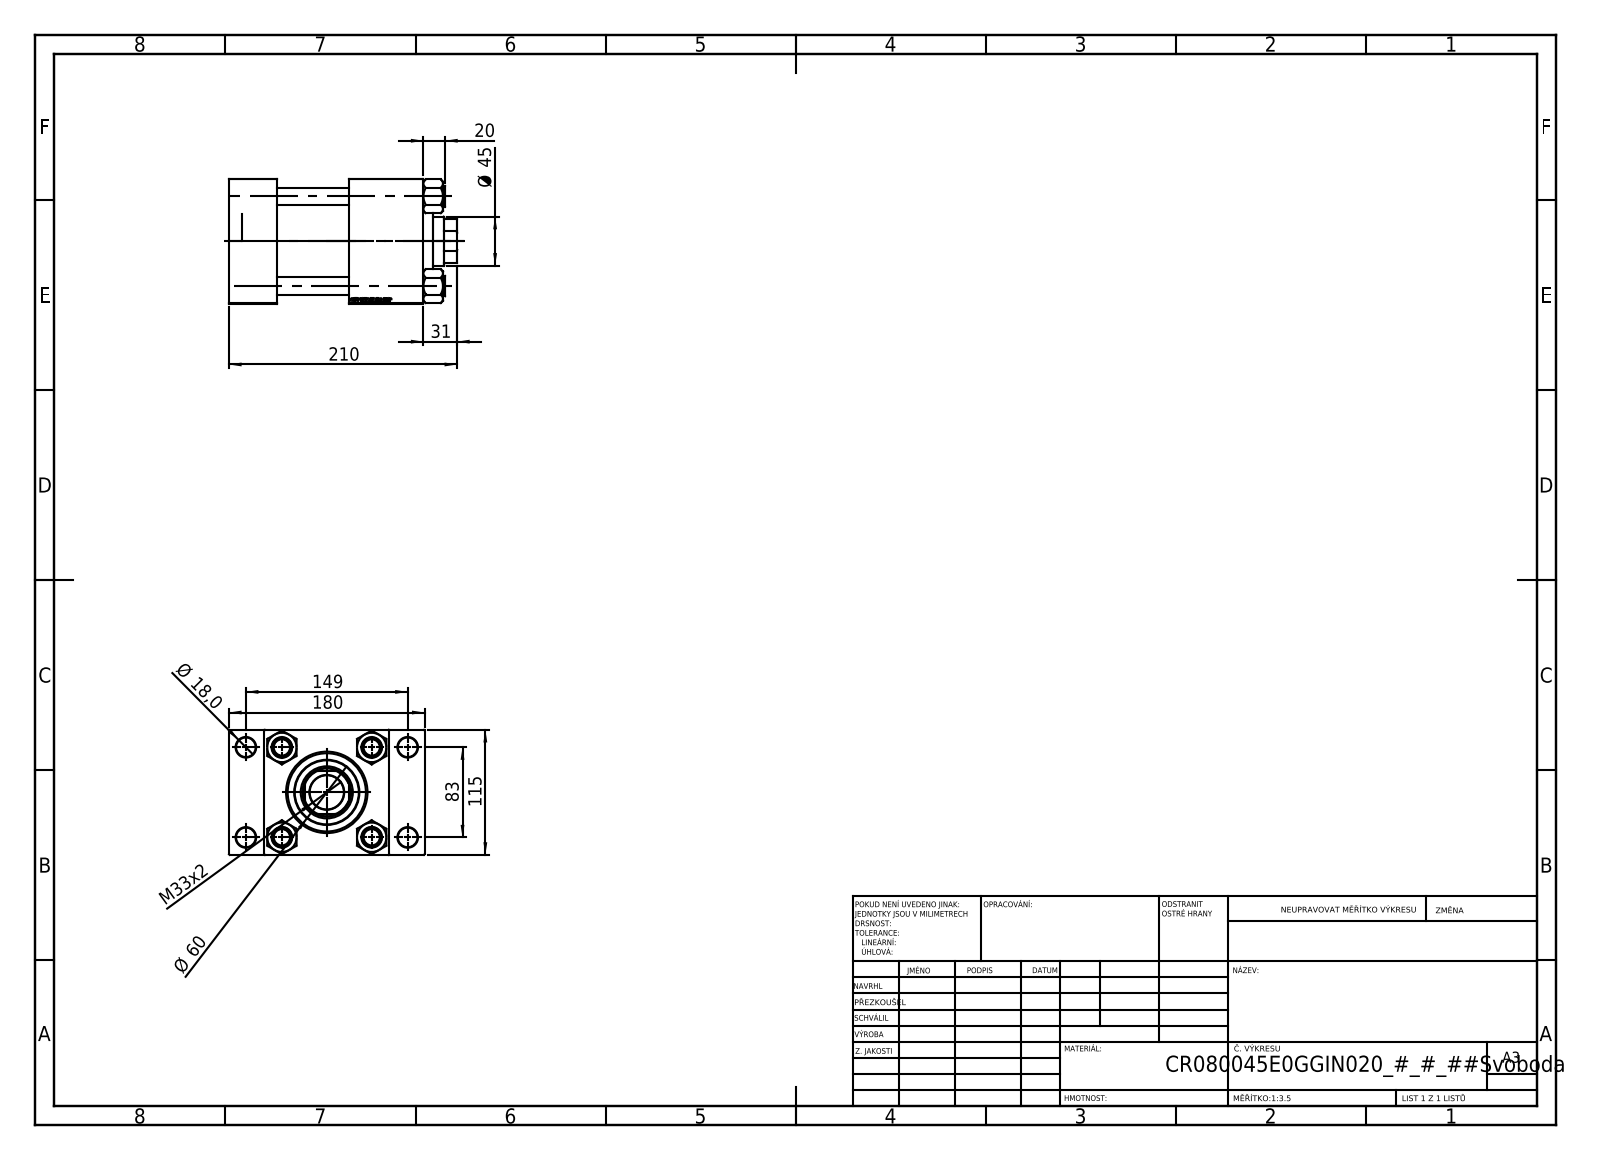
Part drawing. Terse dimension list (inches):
name: NUT_M5_E; V215CR_TYCINKA_E; V215_VC_A; V215CR_E_Body (+1 more)
written by: SolidWorks 2019 (CONFIG_CONTROL_DESIGN)
unit: in
bodies: 11 solids, 1185 faces (546 planar, 87 cylindrical, 552 other)
size: 8.268 × 7.087 × 4.528
volume: 129.3 in³; area: 488.2 in²
holes: 4× ⌀0.63, 4× ⌀0.709, 2× ⌀0.276, 2× ⌀1.041, 2× ⌀1.378, 1× ⌀1.24, 1× ⌀1.772, 1× ⌀1.89, 1× ⌀2.402, 1× ⌀2.835, 1× ⌀3.15
bosses: 4× ⌀0.748, 1× ⌀3.386, 1× ⌀2.362
rounds: 1× R0.866
face distances: 4.528, 1.732, 7.047, 5.315, 1.28, 5.807, 4.331, 2.598, 2.717, 7.087
hole spacings: 1.305, 2.302, 3.256, 3.357, 3.513, 4.561, 5.607, 3.268
